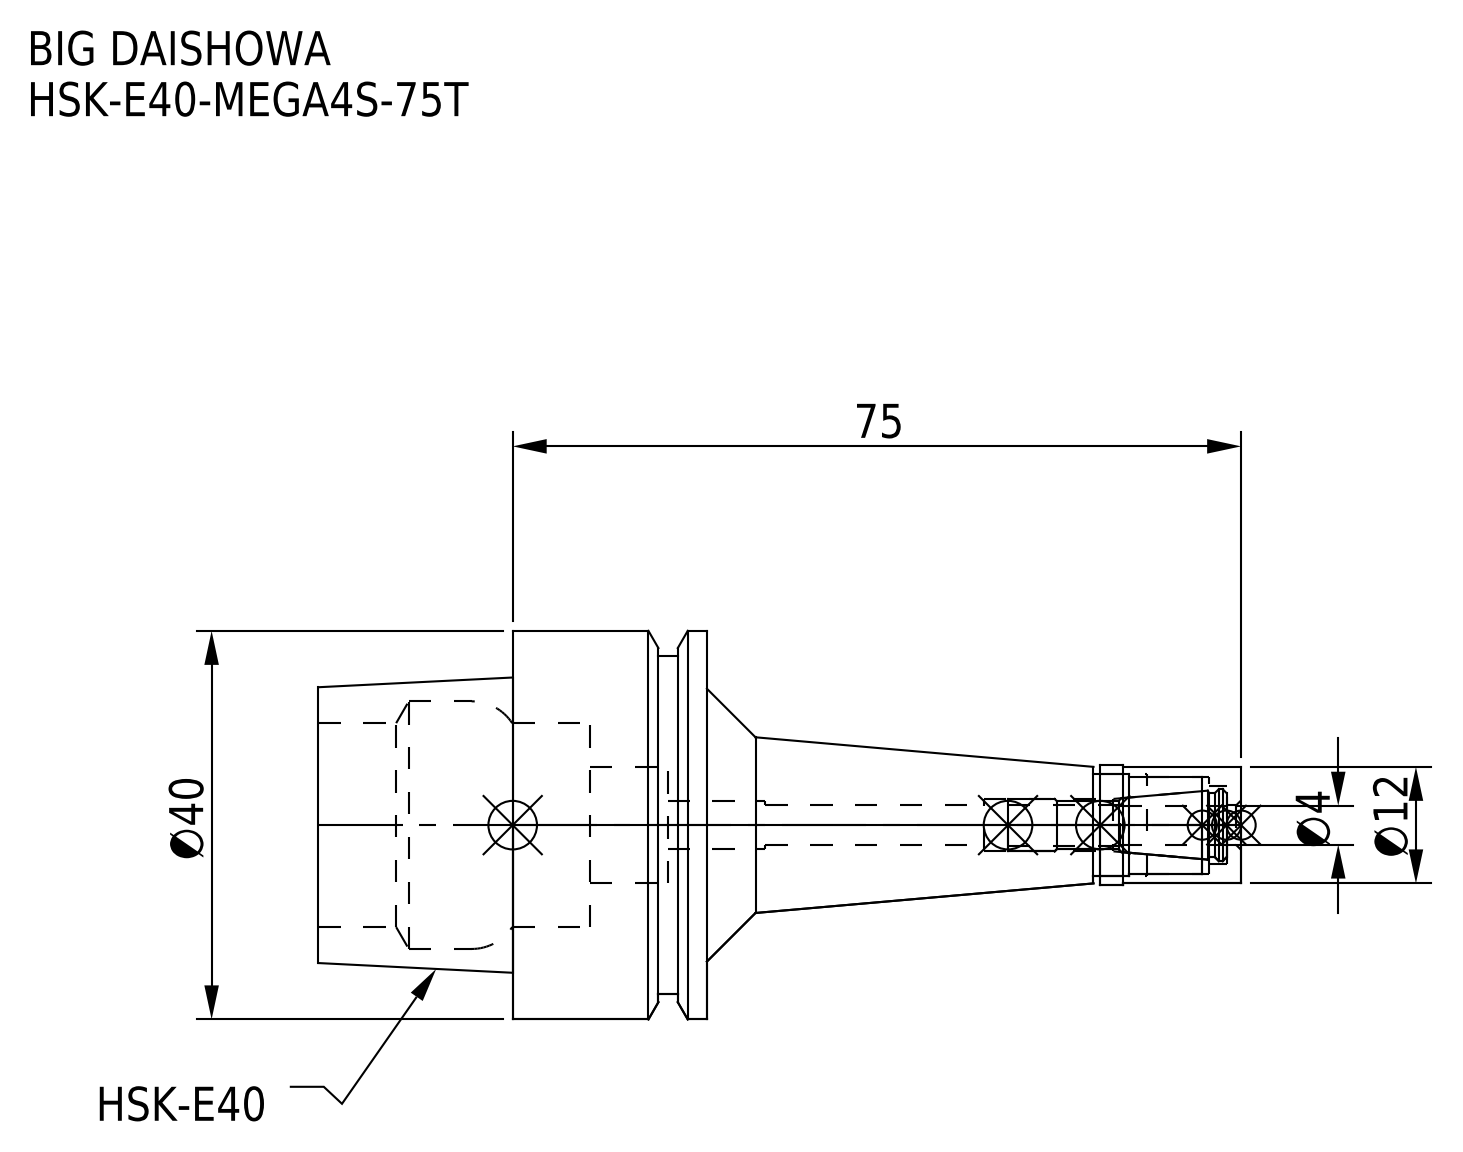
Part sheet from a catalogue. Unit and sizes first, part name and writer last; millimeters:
Units: millimetres
Overall size (bounding box): 95 × 40 × 40
Round holes (diameter × count): ⌀4.1 ×1, ⌀5 ×1, ⌀5.4 ×1, ⌀8 ×1, ⌀10 ×1, ⌀10.5 ×1, ⌀12 ×1, ⌀21 ×1, ⌀25.5 ×1
Round bosses / shafts (diameter × count): ⌀40 ×1, ⌀34.8 ×1, ⌀12.3 ×1
Main face-to-face distances: 20, 40, 12.05, 7.95, 27.95, 3, 15, 4.05, 8, 15.95
Volume: 34 508 mm³ · Surface area: 13 615 mm²
Bodies: 2 solids, 74 faces (18 planar, 38 cylindrical, 18 other)
Part name (STEP PRODUCT): MGN4S_1.stp; HSK-E40-MEGA4S-75T-040-FreeParts; DXF_TEMP_ASSY_ASM_4_ASM.stp; HSK-E40-MEGA4S-75T-040.stp (+3 more)
STEP written by: SolidWorks 2019 (CONFIG_CONTROL_DESIGN)
